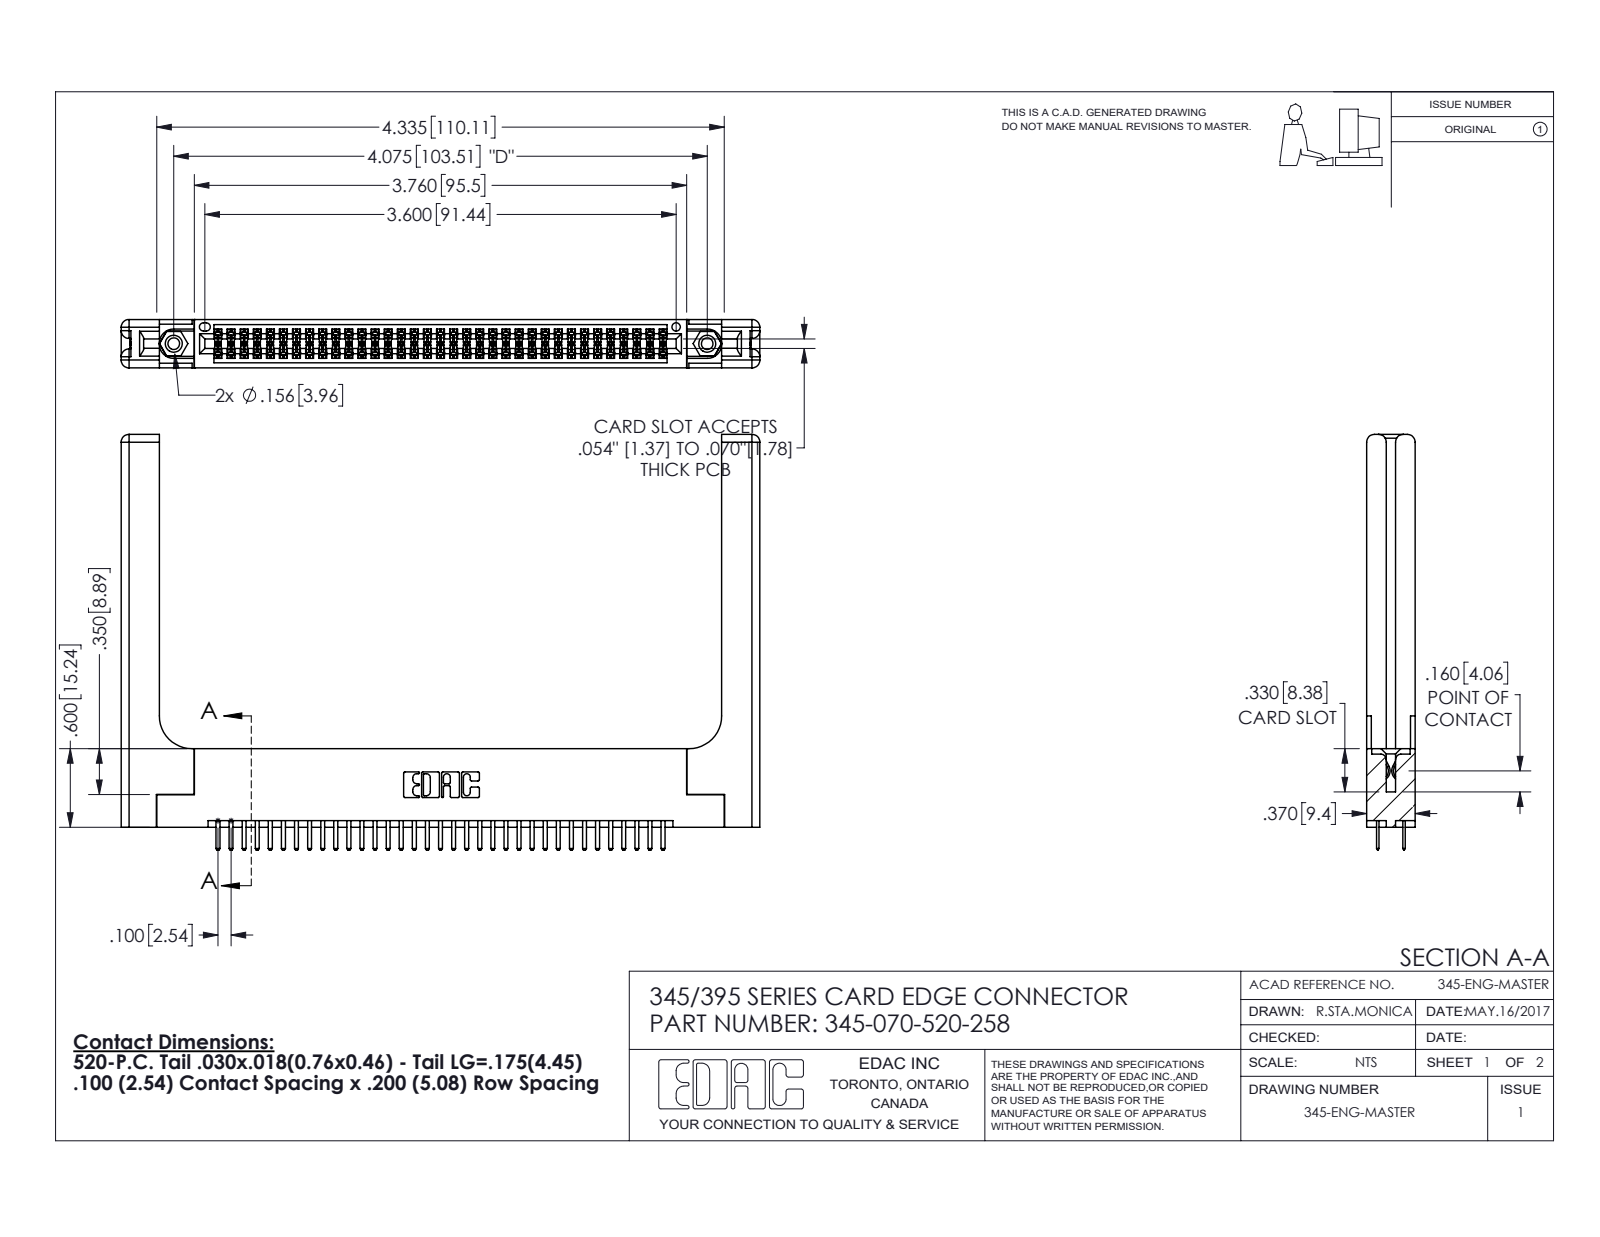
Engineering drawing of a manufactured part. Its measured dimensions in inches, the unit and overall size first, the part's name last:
Units: inches
Overall size (bounding box): 4.879 × 3.175 × 0.37
Round holes (diameter × count): ⌀0.089 ×2, ⌀0.125 ×2, ⌀0.156 ×2, ⌀0.064 ×1
Round bosses / shafts (diameter × count): ⌀0.155 ×2
Partial cylindrical surfaces — rounded edges, fillets, slot ends (radius × count): R0.006 ×105, R0.01 ×74, R0.01 ×22, R0.06 ×16, R0.007 ×6, R0.031 ×6, R0.026 ×3, R0.014 ×2
Main face-to-face distances: 0.37, 0.072, 0.298, 0.2, 0.098, 0.272, 0.025, 0.225, 0.148, 0.15
Hole centre spacings: 0.27, 3.839, 4.075
Volume: 1.246 in³ · Surface area: 34.89 in²
Bodies: 75 solids, 4162 faces (2678 planar, 1424 cylindrical, 60 other)
Part name (STEP PRODUCT): 345 Part_Flush Mounting Lugs - 0.156 Dia-TH; 345-250-001_345-250-001-102; 345-070-520-258; 345-292-001_345-293-120 (+1 more)
STEP written by: SolidWorks 2016 (CONFIG_CONTROL_DESIGN)
